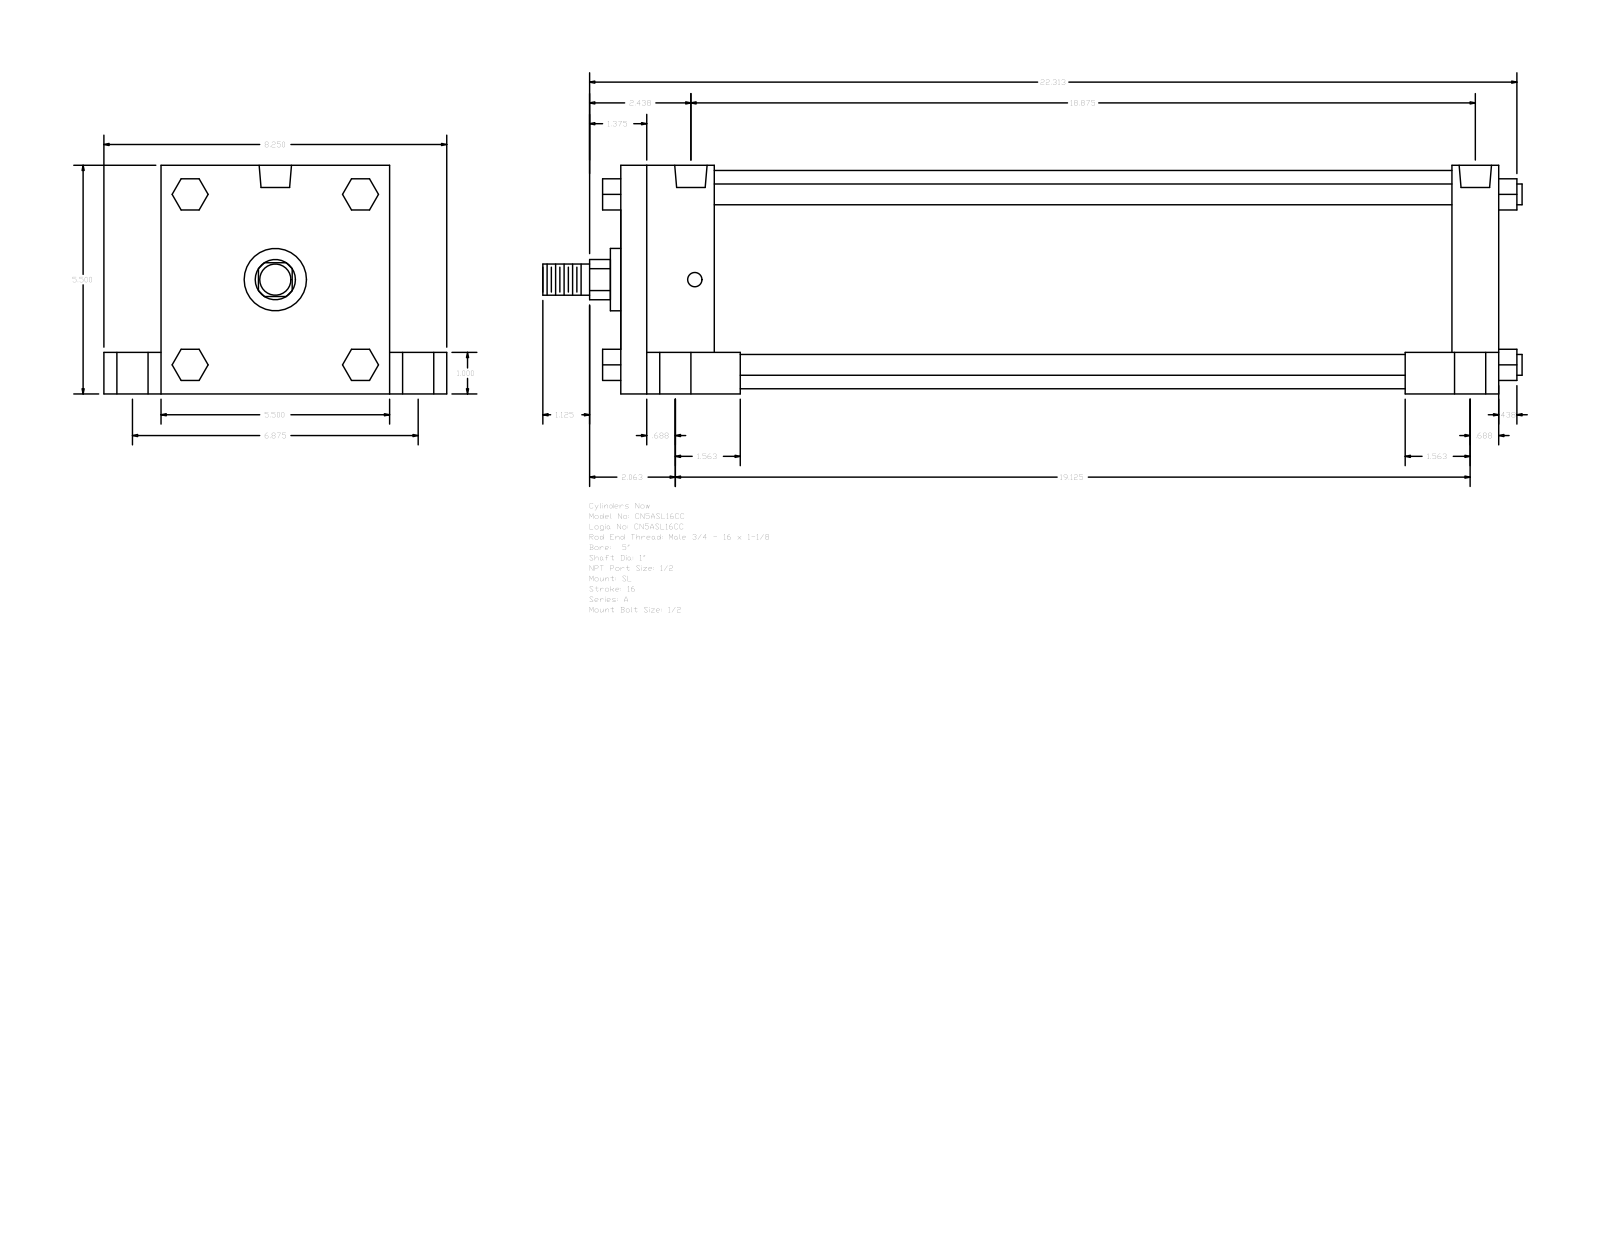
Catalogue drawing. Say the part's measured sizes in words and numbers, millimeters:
The part is named "A_SL__0500_1". Its 3-D file was written by "GSSL Pune (CONFIG_CONTROL_DESIGN)". It is 0 solids with 150 faces: 114 planar, 36 cylindrical and 0 other. Overall it measures 598.49 by 209.55 by 139.7 millimeters. Round holes: 4 of diameter 8.73, 4 of diameter 19.05, 4 of diameter 25.4, 2 of diameter 19.77. Round bosses or shafts: 4 of diameter 12.7, 1 of diameter 133.35, 1 of diameter 38.1, 1 of diameter 25.4, 1 of diameter 19.05. Partial cylindrical surfaces (rounded edges, fillets, slot ends): 1 of radius 12.29. The main face-to-face distances are 139.7, 536.57, 28.57, 25.4, 114.3, 34.93, 174.63, 57.15, 508, 450.85. The hole center spacings are 2.39, 87.31, 87.37, 87.83, 88.12, 174.62, 474.65, 477.04.
